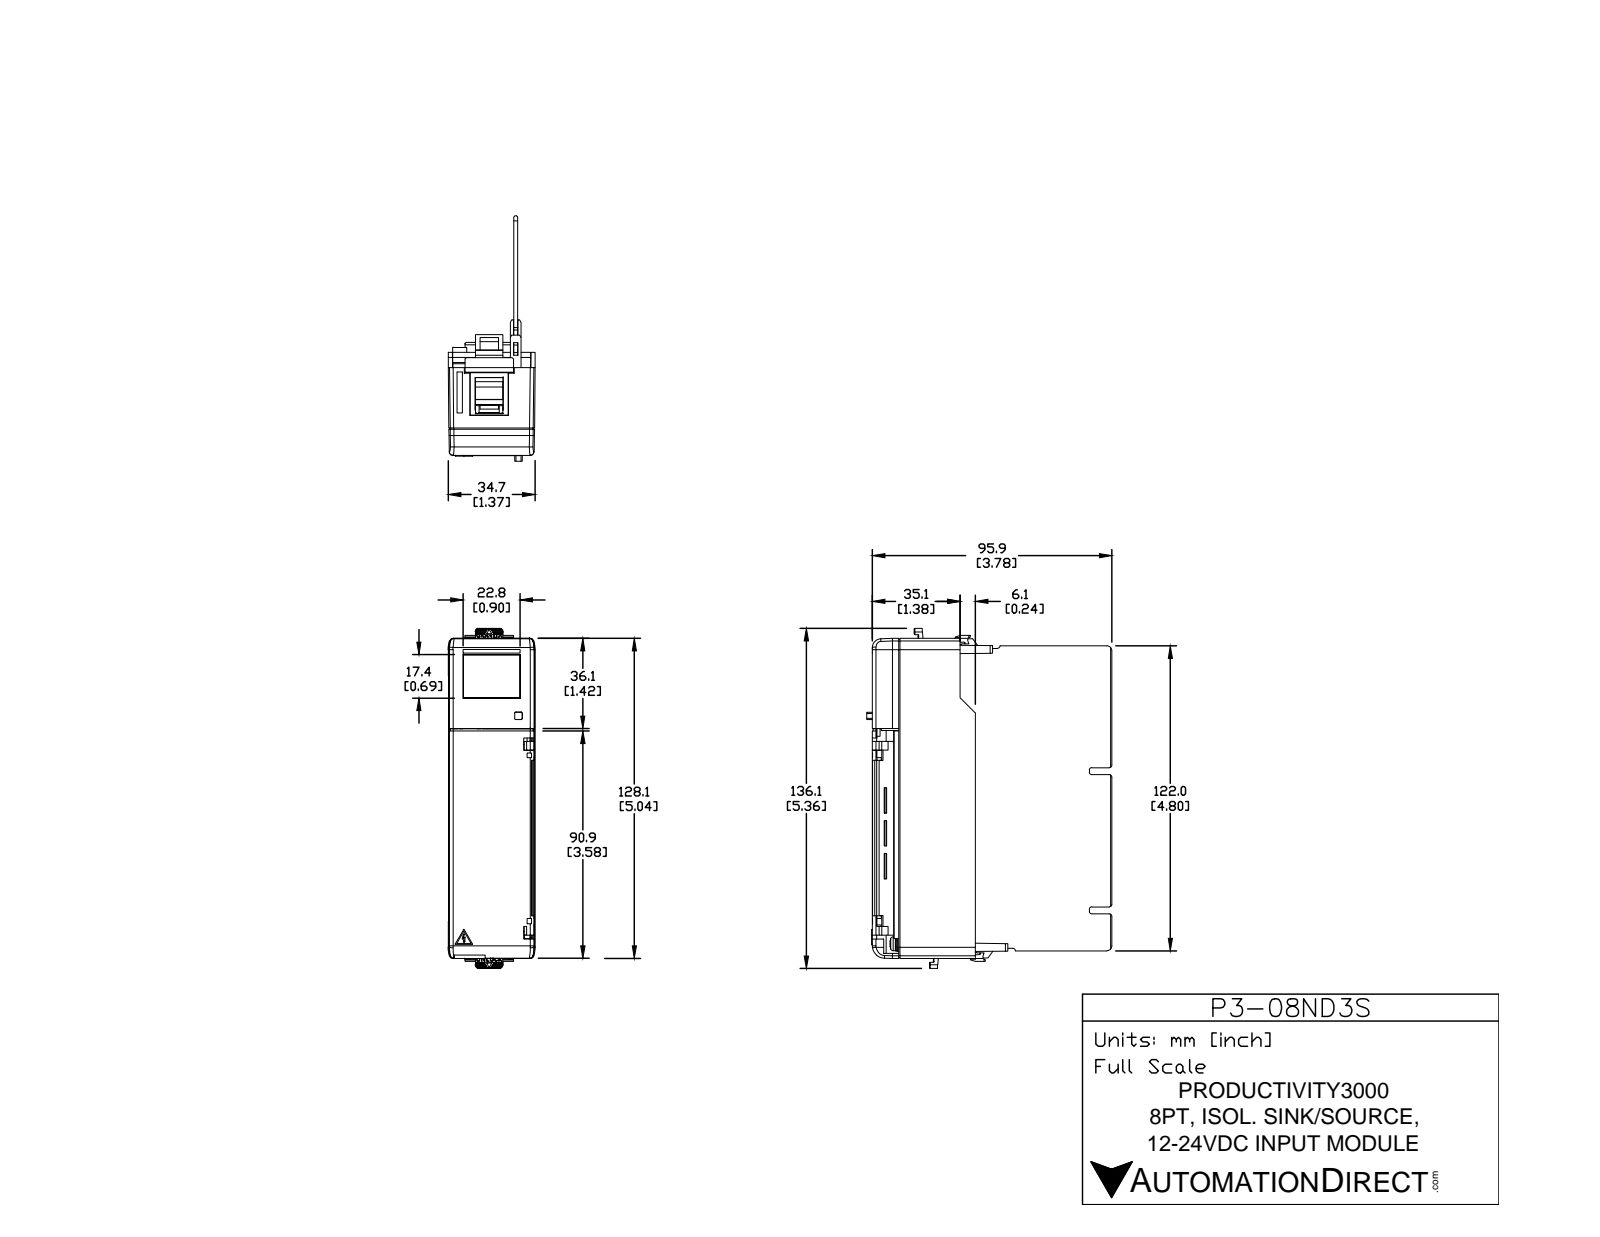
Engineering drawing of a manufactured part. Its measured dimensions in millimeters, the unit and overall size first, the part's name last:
Units: millimetres
Overall size (bounding box): 136.08 × 96.19 × 34.8
Round holes (diameter × count): ⌀3.2 ×22, ⌀5 ×2, ⌀1.8 ×1
Round bosses / shafts (diameter × count): ⌀5.5 ×22, ⌀3 ×22, ⌀2.4 ×20, ⌀5.6 ×2, ⌀2.2 ×2, ⌀2 ×2, ⌀1.5 ×1
Partial cylindrical surfaces — rounded edges, fillets, slot ends (radius × count): R0.5 ×91, R1 ×33, R0.3 ×29, R1.67 ×22, R1.5 ×13, R2 ×6, R0.2 ×5, R0.1 ×4
Main face-to-face distances: 1.6, 1.7, 28.23, 26.53, 32.56, 22.2, 2.2, 7.9, 6.8, 5.32
Hole centre spacings: 8.68, 7.62, 13.84, 15.24, 20.59, 22.86, 27.79, 30.48
Volume: 101 334 mm³ · Surface area: 75 406 mm²
Bodies: 1 solid, 3804 faces (2821 planar, 737 cylindrical, 246 other)
Part name (STEP PRODUCT): P3-08ND3S
STEP written by: SolidWorks 2009 (CONFIG_CONTROL_DESIGN)
